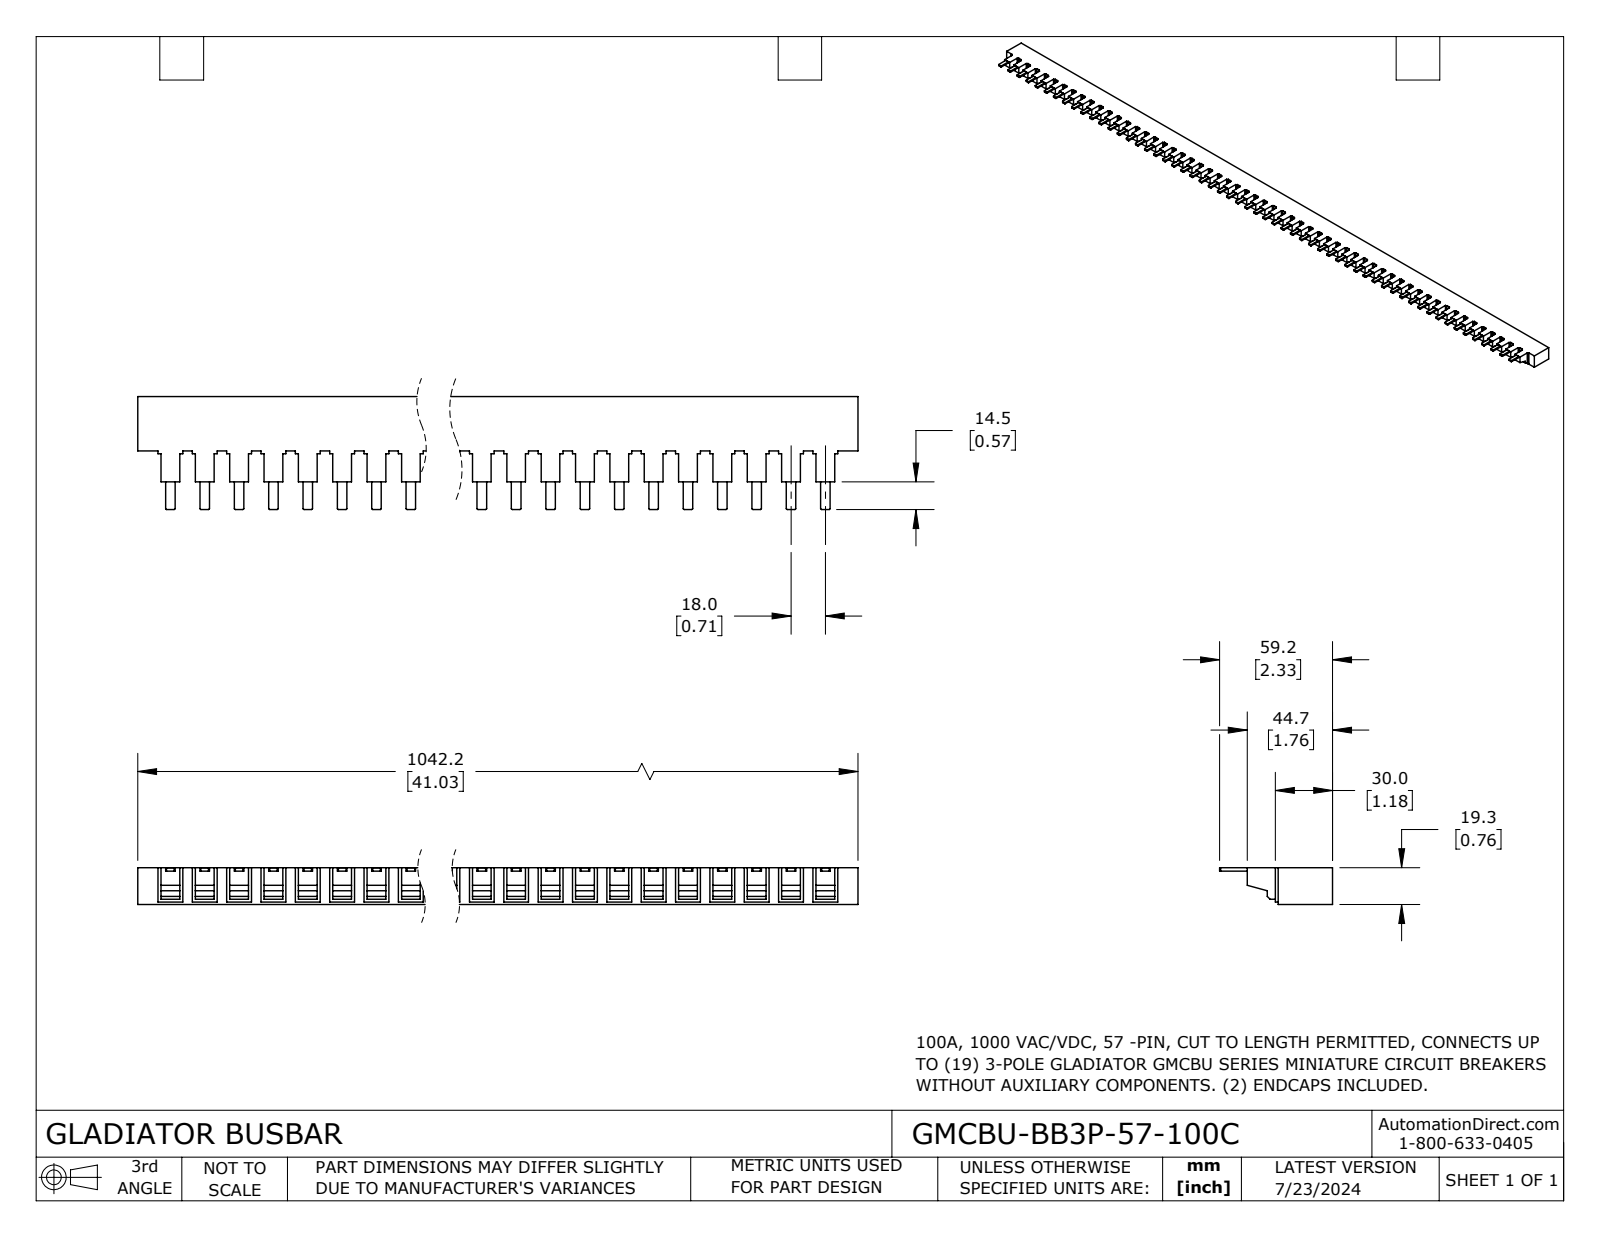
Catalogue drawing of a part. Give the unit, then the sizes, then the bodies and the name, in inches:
Units: inches
Overall size (bounding box): 41.031 × 2.331 × 0.76
Main face-to-face distances: 0.76, 1.122, 0.059, 1.76, 0.638, 0.709, 1.181, 0.579, 0.071, 0.689
Volume: 42.79 in³ · Surface area: 236 in²
Bodies: 1 solid, 1032 faces (1032 planar, 0 cylindrical, 0 other)
Part name (STEP PRODUCT): GMCBU-BB3P-57-100C
STEP written by: SolidWorks 2023 (CONFIG_CONTROL_DESIGN)
